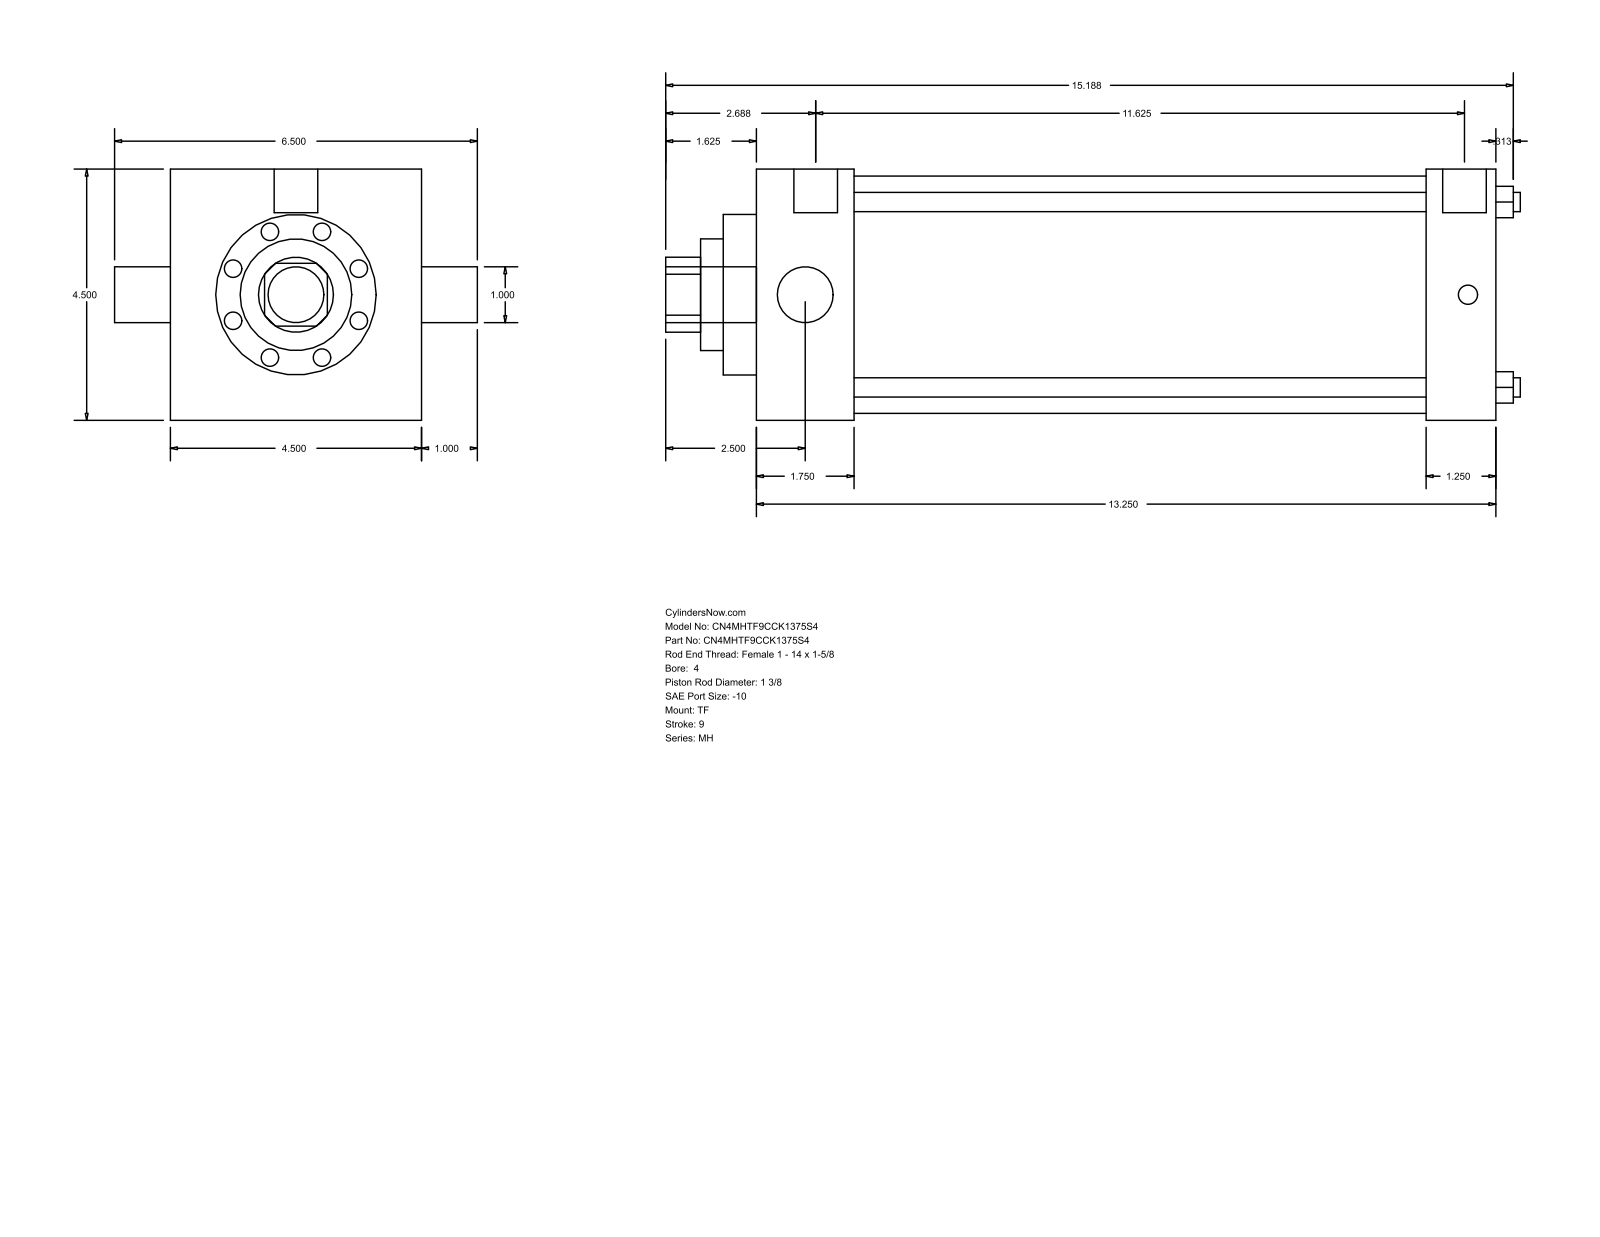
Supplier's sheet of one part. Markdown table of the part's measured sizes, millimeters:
| quantity | value |
| --- | --- |
| part name | MH_TF__0400_1.375 |
| STEP written by | GSSL Pune (CONFIG_CONTROL_DESIGN) |
| units | millimeters |
| bodies | 0 solids, 86 faces (61 planar, 25 cylindrical, 0 other) |
| overall size | 388.94 × 165.1 × 114.3 |
| round holes (diameter × count) | 8.76 × 4, 25.4 × 1, 34.92 × 1, 50.8 × 1, 73.03 × 1, 107.95 × 1 |
| round bosses / shafts (diameter × count) | 8.73 × 3, 19.84 × 2, 25.4 × 1 |
| partial cylindrical surfaces (radius × count) | 17.06 × 1 |
| main face-to-face distances | 114.3, 336.55, 44.45, 292.1, 304.8, 260.35, 31.75, 15.08, 59.53, 319.88 |
| hole center spacings | 59.62, 84.32, 119.25 |
